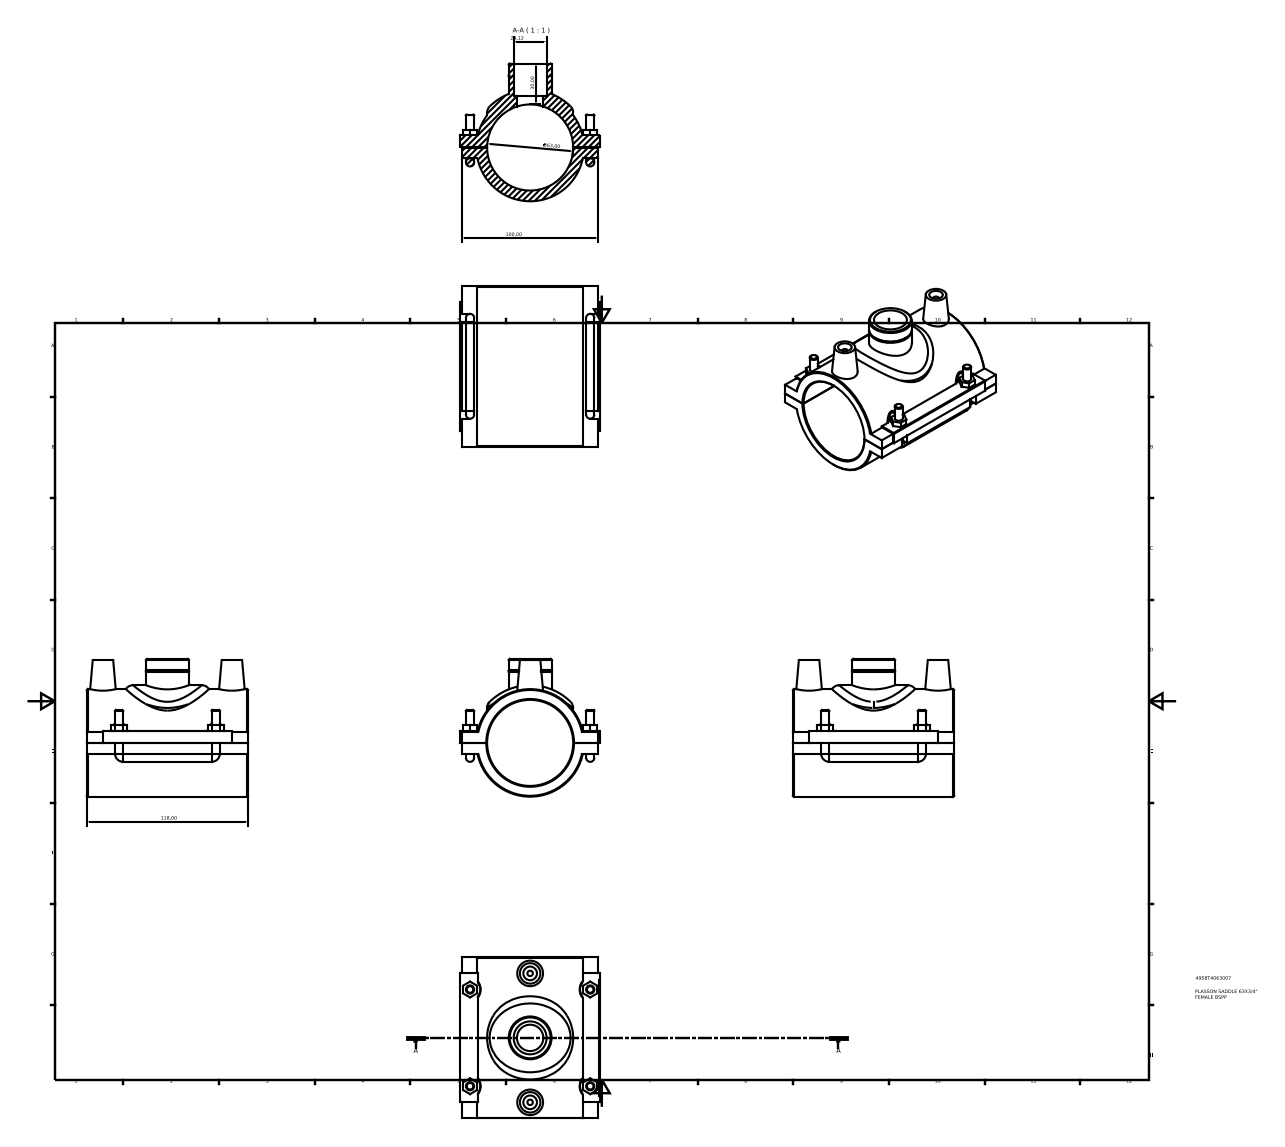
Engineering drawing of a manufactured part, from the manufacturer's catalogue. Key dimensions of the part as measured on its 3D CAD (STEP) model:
Part name (STEP PRODUCT): 4958T4063007
STEP written by: Autodesk Inventor 2015 (AUTOMOTIVE_DESIGN)
Units: millimetres
Bodies: 1 solid, 139 faces (82 planar, 31 cylindrical, 26 other)
Overall size (bounding box): 118 × 102 × 100.88
Volume: 276 021 mm³ · Surface area: 82 486 mm²
Round holes (diameter × count): ⌀10 ×2, ⌀19.29 ×1, ⌀24.12 ×1, ⌀63 ×1
Round bosses / shafts (diameter × count): ⌀6 ×6, ⌀4 ×2, ⌀78.75 ×1, ⌀31.35 ×1, ⌀30.35 ×1
Partial cylindrical surfaces — rounded edges, fillets, slot ends (radius × count): R7.5 ×4, R0.5 ×1, R31.5 ×1, R42.21 ×1
Main face-to-face distances: 7.83, 7.93, 1, 16.75, 8.92, 8.82, 118, 101, 100, 102
Hole centre spacings: 47.2, 94.4
